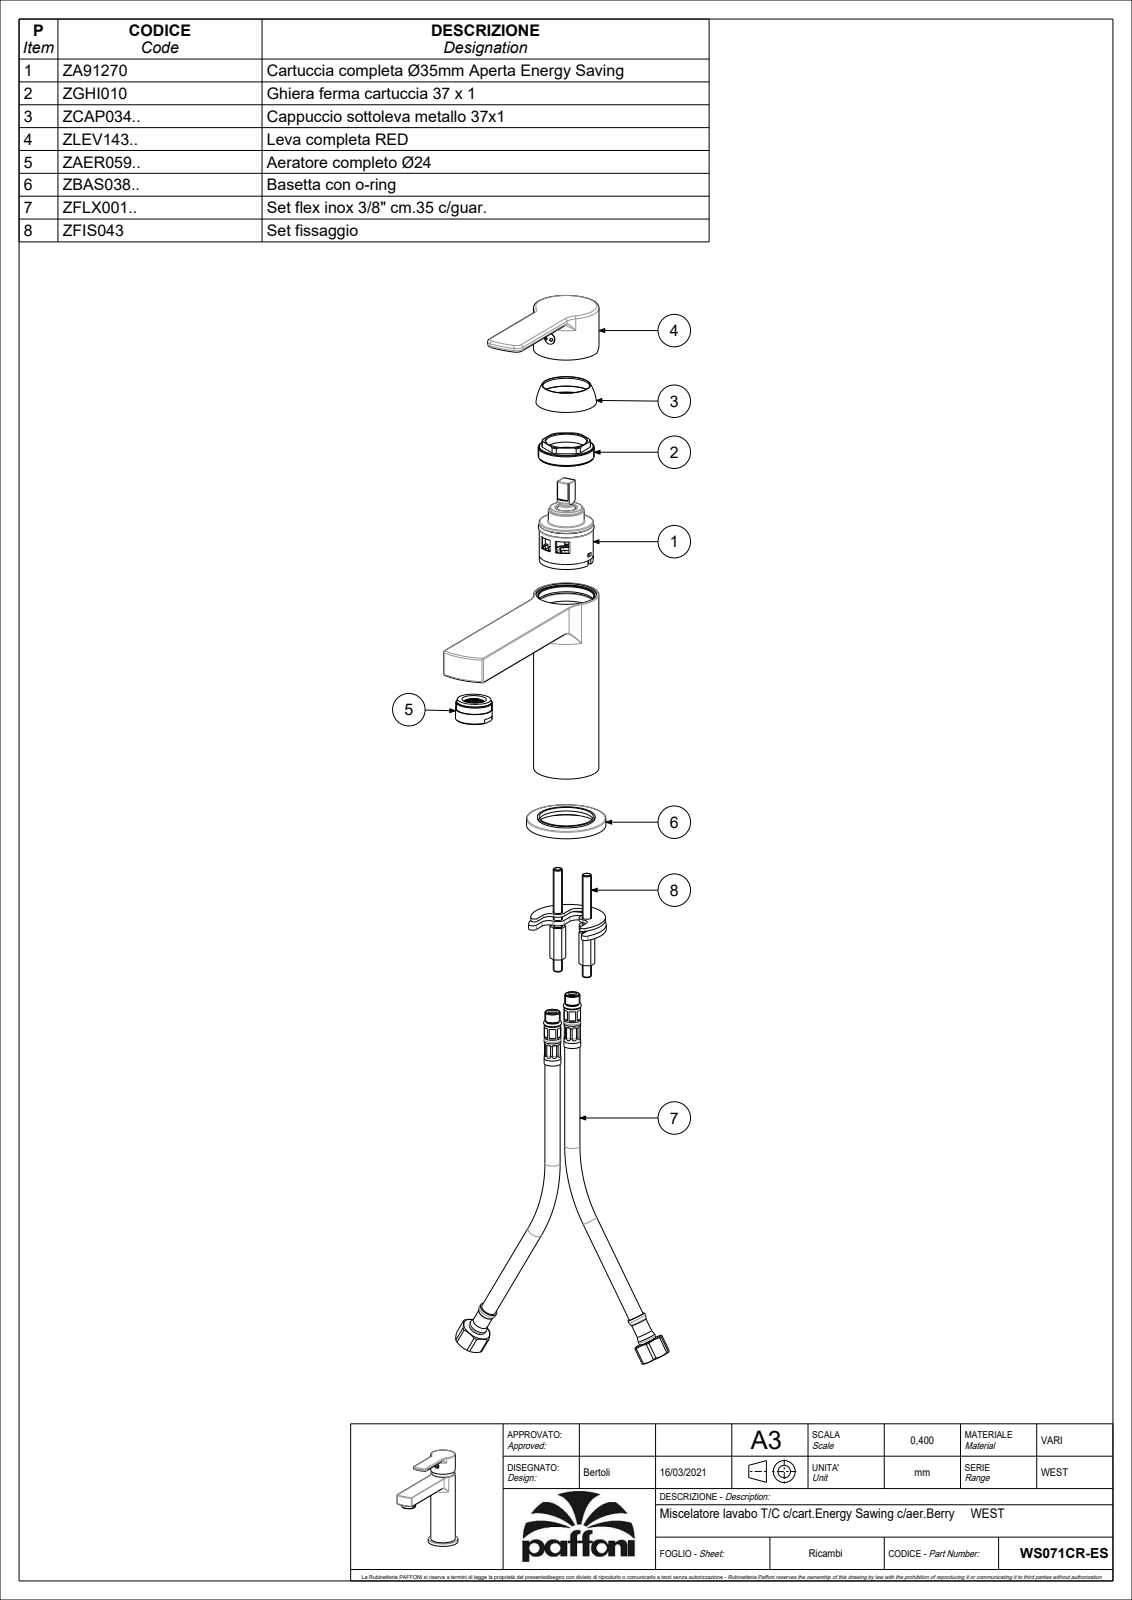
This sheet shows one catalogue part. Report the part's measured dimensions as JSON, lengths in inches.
{"part_name": "WS075CR", "step_written_by": "CREO PARAMETRIC BY PTC INC, 2020044 (CONFIG_CONTROL_DESIGN)", "units": "inches", "bodies": {"solids": 2, "faces": 3325, "planar": 2379, "cylindrical": 525, "other": 421}, "overall_size": [6.457, 6.4, 2.047], "volume_in3": 9.944, "surface_area_in2": 162.3, "round_holes": [[0.217, 3], [0.197, 2], [0.276, 2], [0.315, 2], [0.354, 2], [0.433, 2], [0.118, 1], [0.134, 1], [0.138, 1], [0.157, 1], [0.177, 1], [0.181, 1]], "round_bosses_or_shafts": [[0.189, 2], [2.047, 1], [1.693, 1], [1.685, 1], [1.677, 1], [1.488, 1], [1.394, 1], [1.378, 1]], "partial_cylinders_radius": [[0.02, 87], [0.059, 22], [0.039, 17], [0.079, 9], [0.067, 6], [0.031, 4], [0.197, 4], [0.228, 4]], "face_to_face_distances": [0.118, 0.551, 0.669, 1.419, 2.089, 0.591, 1.063, 0.177, 0.039, 1.911], "hole_center_spacings": [0.535, 0.02, 0.111, 0.339, 0.355, 0.53, 0.53, 0.571]}
